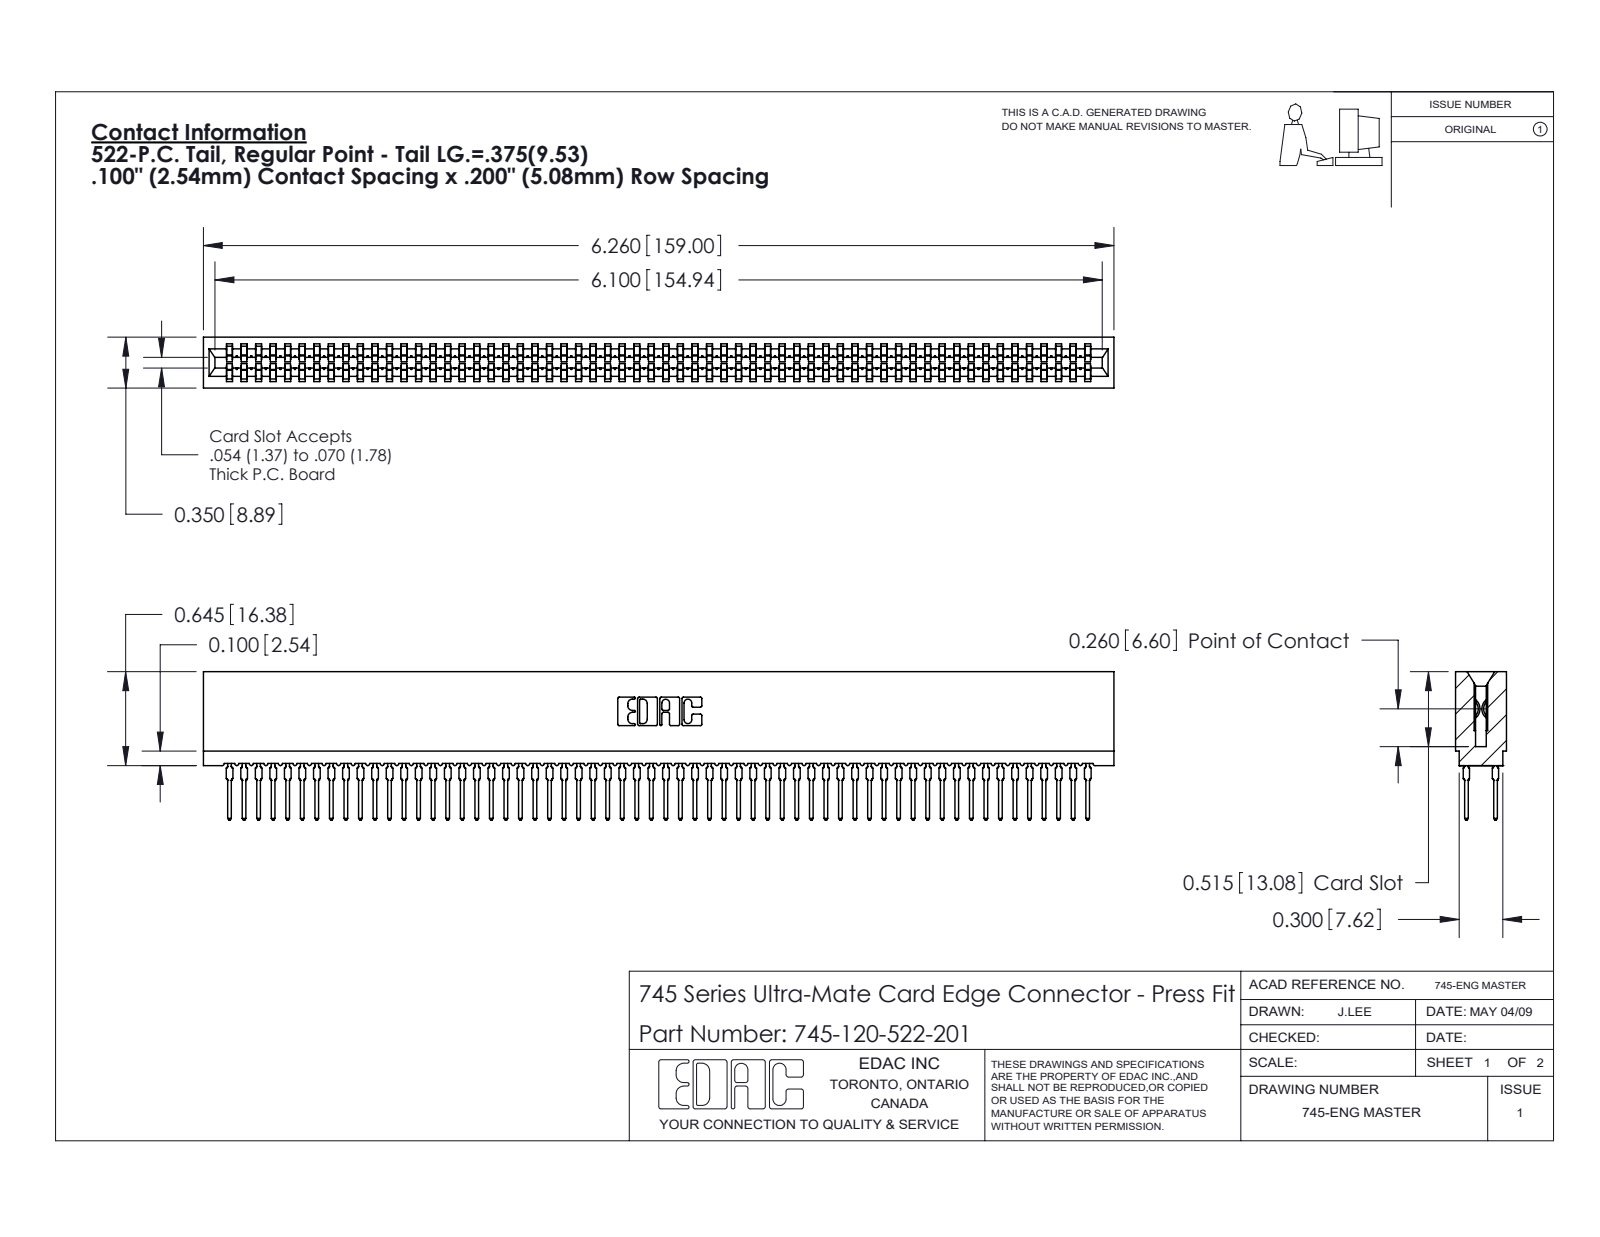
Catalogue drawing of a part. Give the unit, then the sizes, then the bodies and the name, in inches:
Units: inches
Overall size (bounding box): 6.26 × 1.021 × 0.35
Partial cylindrical surfaces — rounded edges, fillets, slot ends (radius × count): R0.021 ×240, R0.015 ×120, R0.01 ×22, R0.005 ×8, R0.011 ×8, R0.007 ×6, R0.031 ×6, R0.026 ×3
Main face-to-face distances: 0.35, 0.063, 0.287, 0.045, 0.305, 0.018, 0.243, 0.138, 0.212, 0.093
Volume: 0.875 in³ · Surface area: 46.47 in²
Bodies: 121 solids, 10835 faces (5575 planar, 2140 cylindrical, 3120 other)
Part name (STEP PRODUCT): 745-120-522-201; 745 Part_Insulator Option - 01; 745-292-001_522
STEP written by: SolidWorks 2020 (CONFIG_CONTROL_DESIGN)
